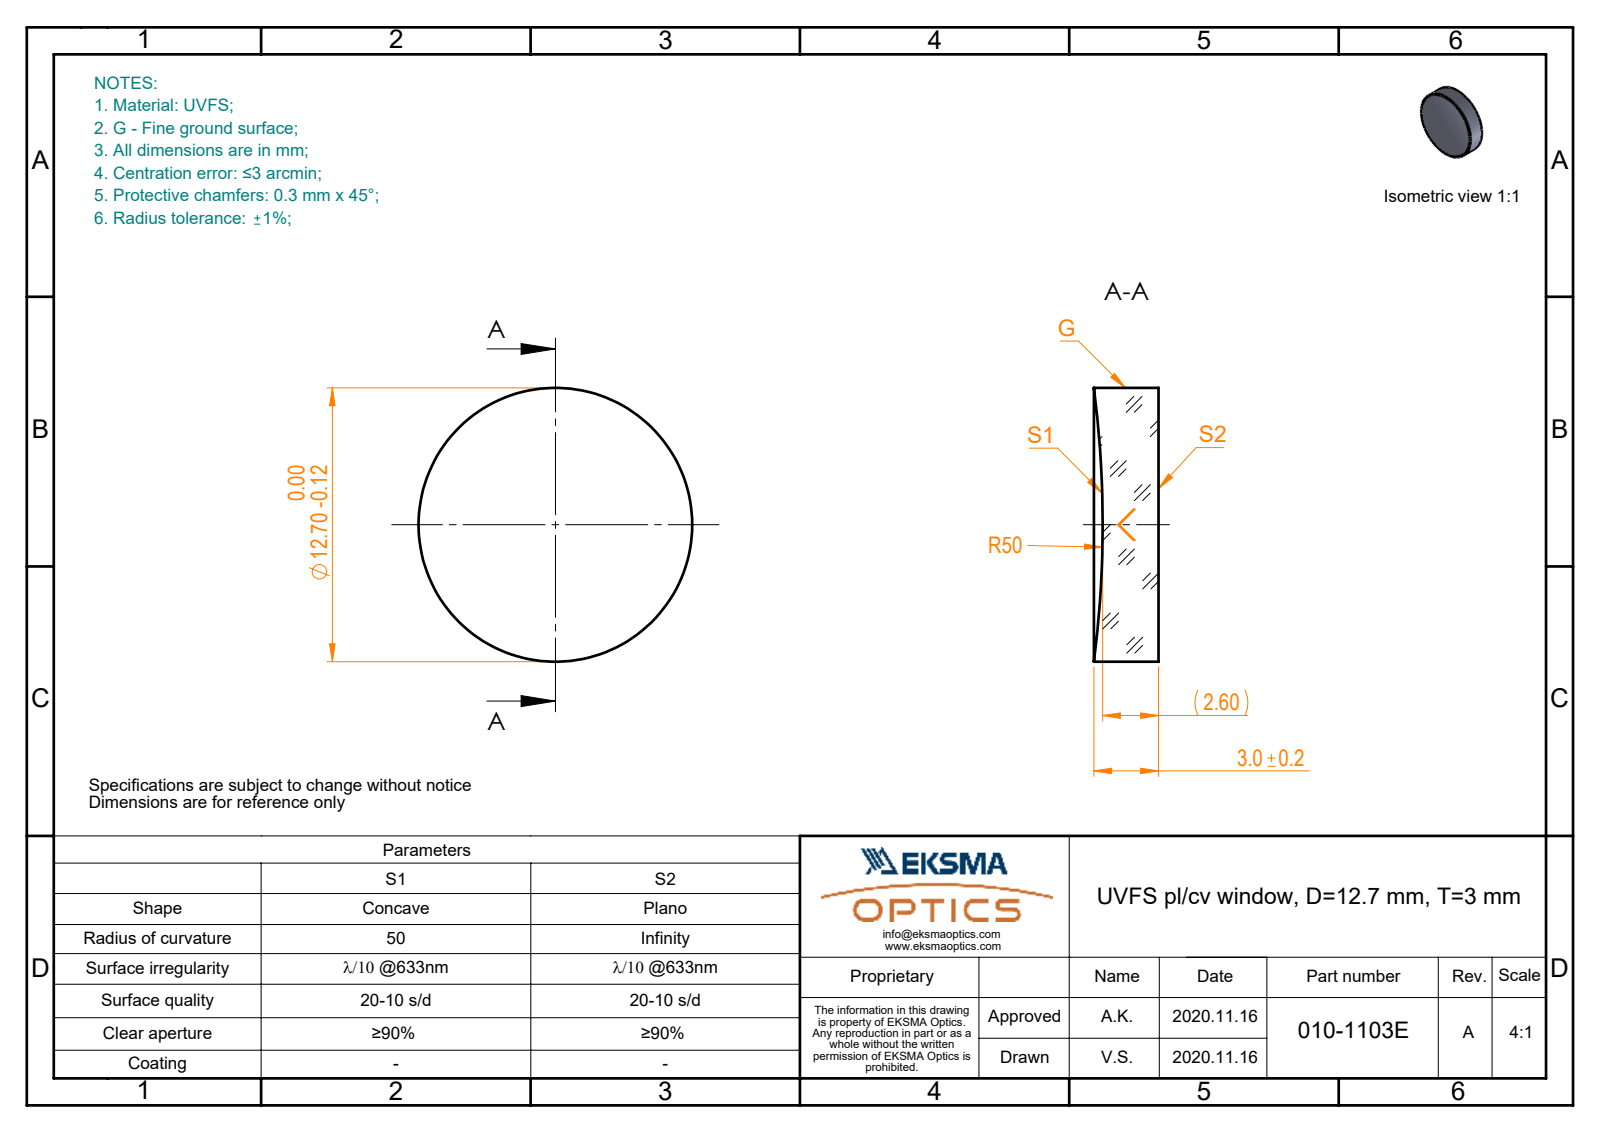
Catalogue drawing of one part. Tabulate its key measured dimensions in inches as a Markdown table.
| quantity | value |
| --- | --- |
| part name | 010-1103E_UVFS_PCV_window |
| STEP written by | SolidWorks 2019 (CONFIG_CONTROL_DESIGN) |
| units | inches |
| bodies | 1 solid, 5 faces (1 planar, 2 cylindrical, 2 other) |
| overall size | 0.5 × 0.5 × 0.118 |
| volume | 0.022 in³ |
| surface area | 0.58 in² |
| round bosses / shafts (diameter × count) | 0.5 × 1 |
